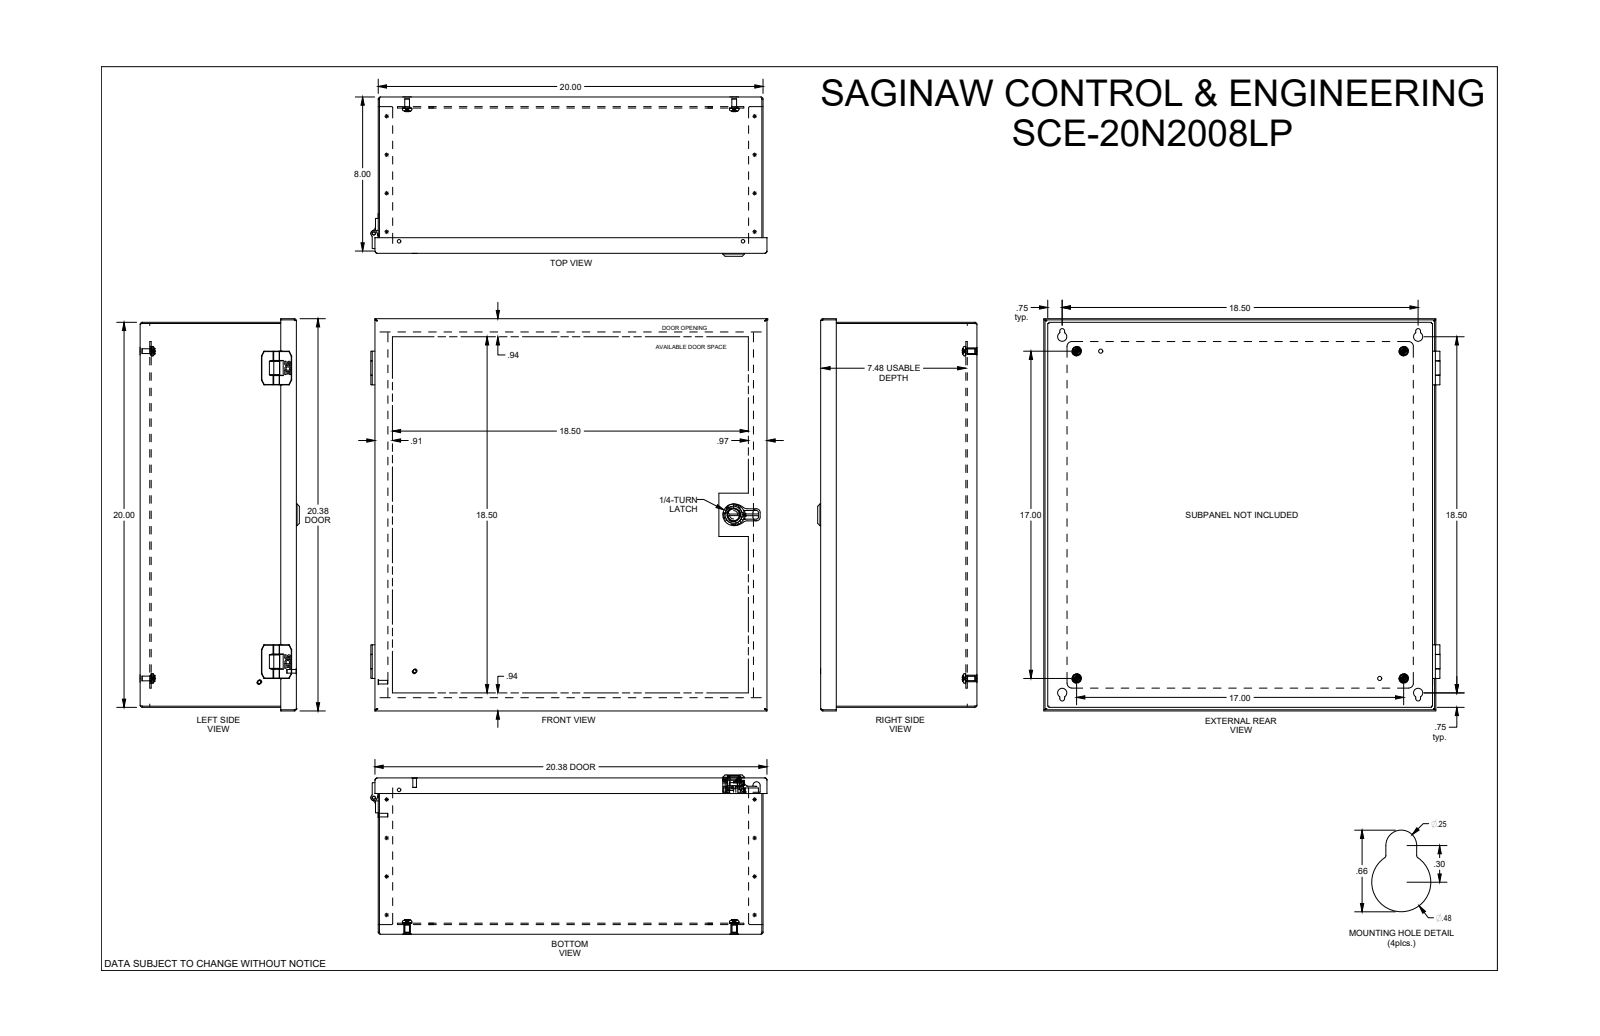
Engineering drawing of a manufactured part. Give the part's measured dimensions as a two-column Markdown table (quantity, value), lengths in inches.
| quantity | value |
| --- | --- |
| part name | SCE-20N2008LP |
| STEP written by | SolidWorks 2019 (CONFIG_CONTROL_DESIGN) |
| units | inches |
| bodies | 0 solids, 3058 faces (1038 planar, 1032 cylindrical, 988 other) |
| overall size | 20.593 × 20.375 × 8.279 |
| round holes (diameter × count) | 0.25 × 4, 0.281 × 4, 0.329 × 4, 0.343 × 4, 0.479 × 4, 0.48 × 4, 0.187 × 2, 0.193 × 2, 0.218 × 2, 0.158 × 1, 0.44 × 1, 0.635 × 1 |
| round bosses / shafts (diameter × count) | 0.492 × 4, 0.341 × 4, 0.248 × 4, 0.237 × 4, 0.17 × 4, 0.16 × 4, 0.135 × 4, 0.108 × 4 |
| partial cylindrical surfaces (radius × count) | 0.01 × 253, 0.106 × 132, 0.005 × 130, 0.02 × 103, 0.015 × 32, 0.025 × 24, 0.052 × 16, 0.112 × 16 |
| main face-to-face distances | 0.06, 8.059, 19.94, 8.119, 7.999, 0.5, 0.44, 0.575, 0.515, 7.484 |
| hole center spacings | 17.766, 1.061, 17, 18.5, 25.102, 1.091, 1.25, 2.136 |
